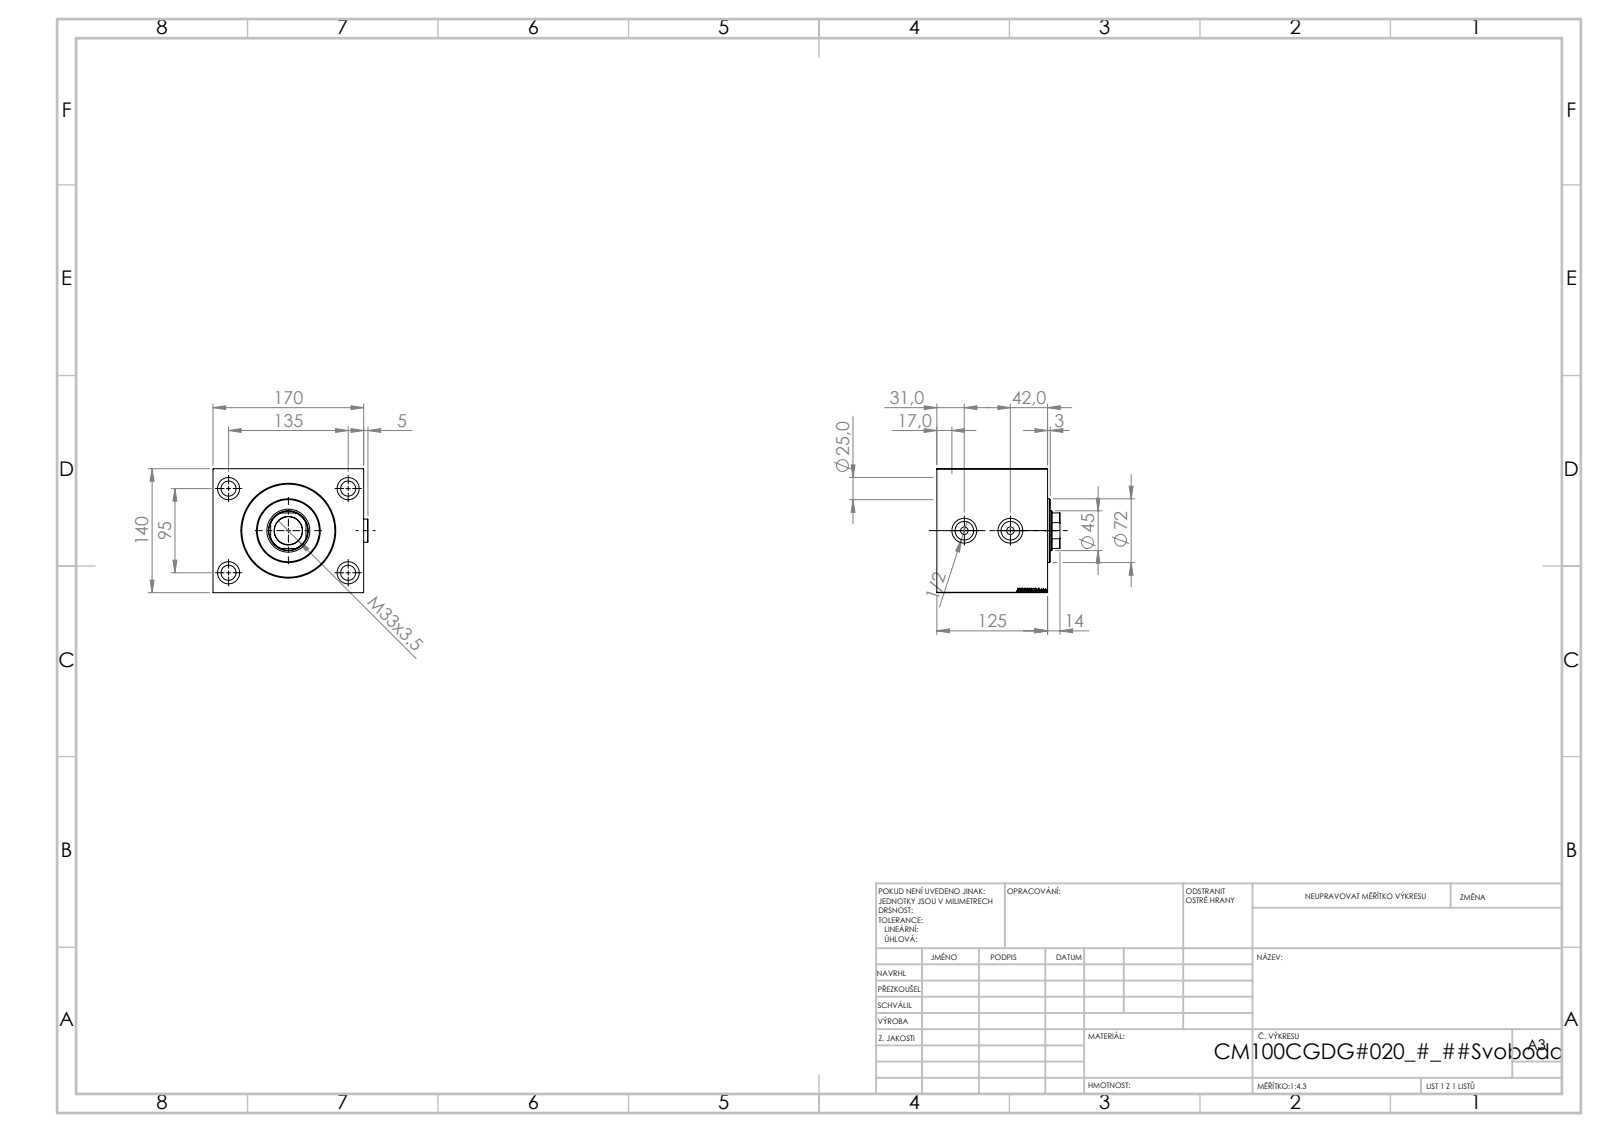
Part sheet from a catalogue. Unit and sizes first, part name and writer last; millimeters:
Units: millimetres
Overall size (bounding box): 174.9 × 140 × 139
Round holes (diameter × count): ⌀17 ×4, ⌀25 ×4, ⌀8.5 ×2, ⌀20.96 ×2, ⌀28 ×2, ⌀31.5 ×1, ⌀45 ×1, ⌀48.5 ×1, ⌀100 ×1, ⌀102 ×1, ⌀105 ×1
Round bosses / shafts (diameter × count): ⌀26 ×2, ⌀72 ×1
Partial cylindrical surfaces — rounded edges, fillets, slot ends (radius × count): R22 ×1
Main face-to-face distances: 140, 125, 170, 51, 74, 21.6, 29.4, 103.4, 10, 31.6
Hole centre spacings: 82.54, 95, 135, 165.08, 52
Volume: 2 734 000 mm³ · Surface area: 237 780 mm²
Bodies: 5 solids, 917 faces (443 planar, 76 cylindrical, 398 other)
Part name (STEP PRODUCT): V450CM_C_Body; V450CM_C_VCP; Zatka_OIL_PORT; V450CM_VC_B
STEP written by: SolidWorks 2019 (CONFIG_CONTROL_DESIGN)
